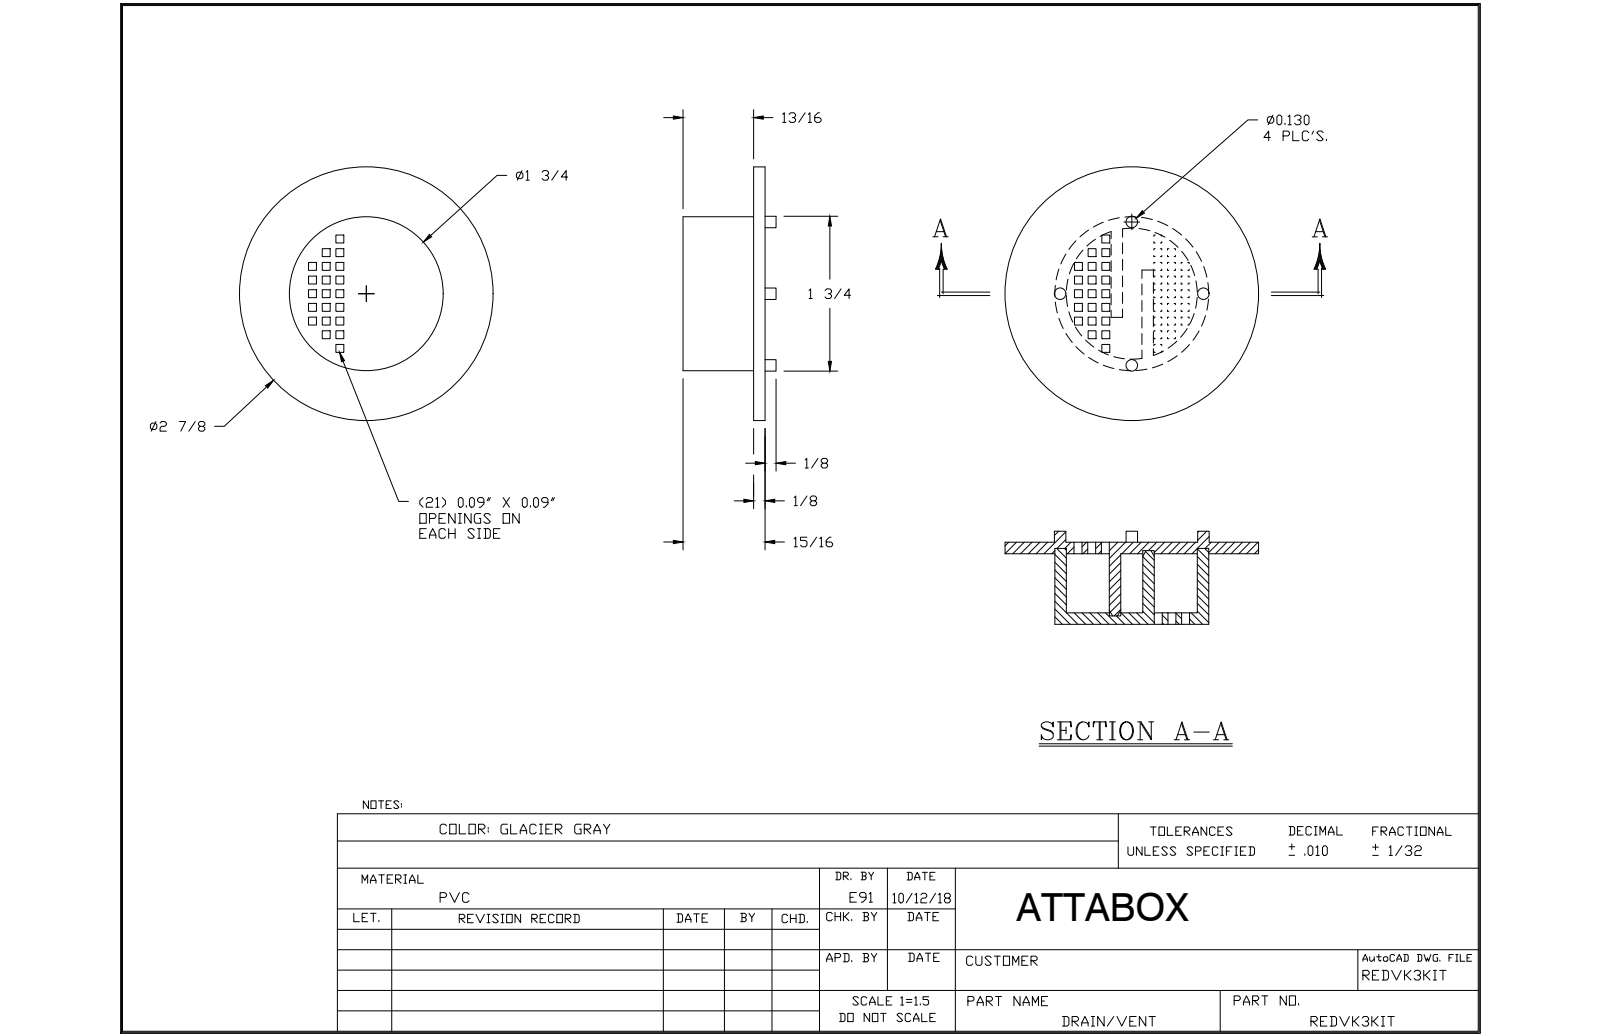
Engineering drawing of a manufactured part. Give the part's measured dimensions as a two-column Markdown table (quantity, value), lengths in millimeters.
| quantity | value |
| --- | --- |
| part name | REDVK3KIT |
| STEP written by | SolidWorks 2017 (AUTOMOTIVE_DESIGN) |
| units | millimeters |
| bodies | 2 solids, 199 faces (190 planar, 9 cylindrical, 0 other) |
| overall size | 57.2 × 57.2 × 25.4 |
| volume | 21 700 mm³ |
| surface area | 16 750 mm² |
| round holes (diameter × count) | 38.1 × 1, 44.5 × 1 |
| round bosses / shafts (diameter × count) | 3.2 × 4, 57.2 × 1 |
| main face-to-face distances | 3.2, 19.1, 22.2, 15.9, 17.4, 1.6, 1.6, 3.2, 20.6, 0.8 |
